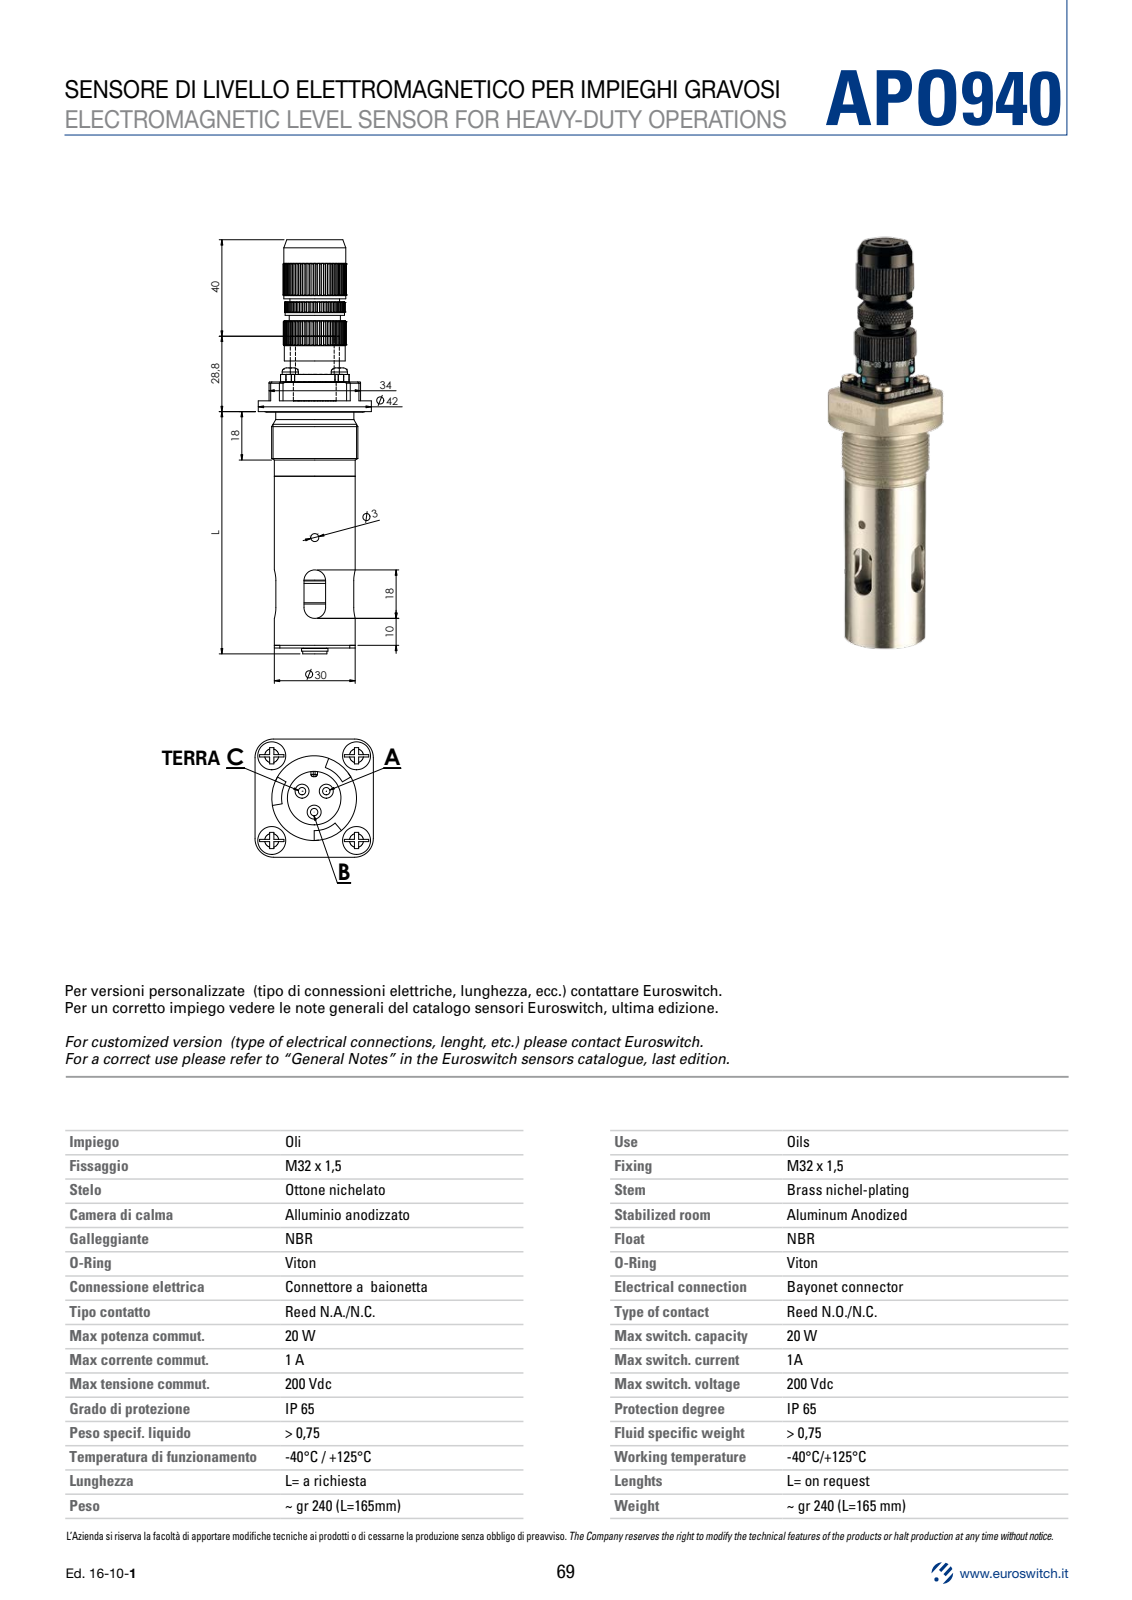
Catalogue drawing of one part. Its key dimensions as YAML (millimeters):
part_name: "AP0940"
step_written_by: "SolidWorks 2019 (AUTOMOTIVE_DESIGN)"
units: millimeters
bodies: {solids: 0, faces: 1133, planar: 671, cylindrical: 216, other: 246}
overall_size: [204.07, 42, 42]
round_holes:
  - {diameter: 3, count: 5}
  - {diameter: 0.8, count: 2}
  - {diameter: 4, count: 2}
  - {diameter: 7.67, count: 1}
  - {diameter: 10, count: 1}
  - {diameter: 11.5, count: 1}
  - {diameter: 13, count: 1}
  - {diameter: 18.5, count: 1}
  - {diameter: 28, count: 1}
  - {diameter: 38.6, count: 1}
round_bosses_or_shafts:
  - {diameter: 6, count: 4}
  - {diameter: 2.6, count: 3}
  - {diameter: 2, count: 3}
  - {diameter: 1.58, count: 3}
  - {diameter: 3.5, count: 2}
  - {diameter: 42, count: 1}
  - {diameter: 33.2, count: 1}
  - {diameter: 32, count: 1}
partial_cylinders:
  - {radius: 0.9, count: 12}
  - {radius: 0.8, count: 8}
  - {radius: 4, count: 6}
  - {radius: 0.5, count: 5}
  - {radius: 6, count: 4}
  - {radius: 1.1, count: 2}
  - {radius: 3.85, count: 2}
  - {radius: 8.5, count: 2}
face_to_face_distances: [11, 69, 58, 3, 9.8, 1.5, 2.8, 15, 32.4, 90.4]
hole_center_spacings: [2.5, 4.33, 6.94, 9, 9.34, 11.24, 4.34, 18]
